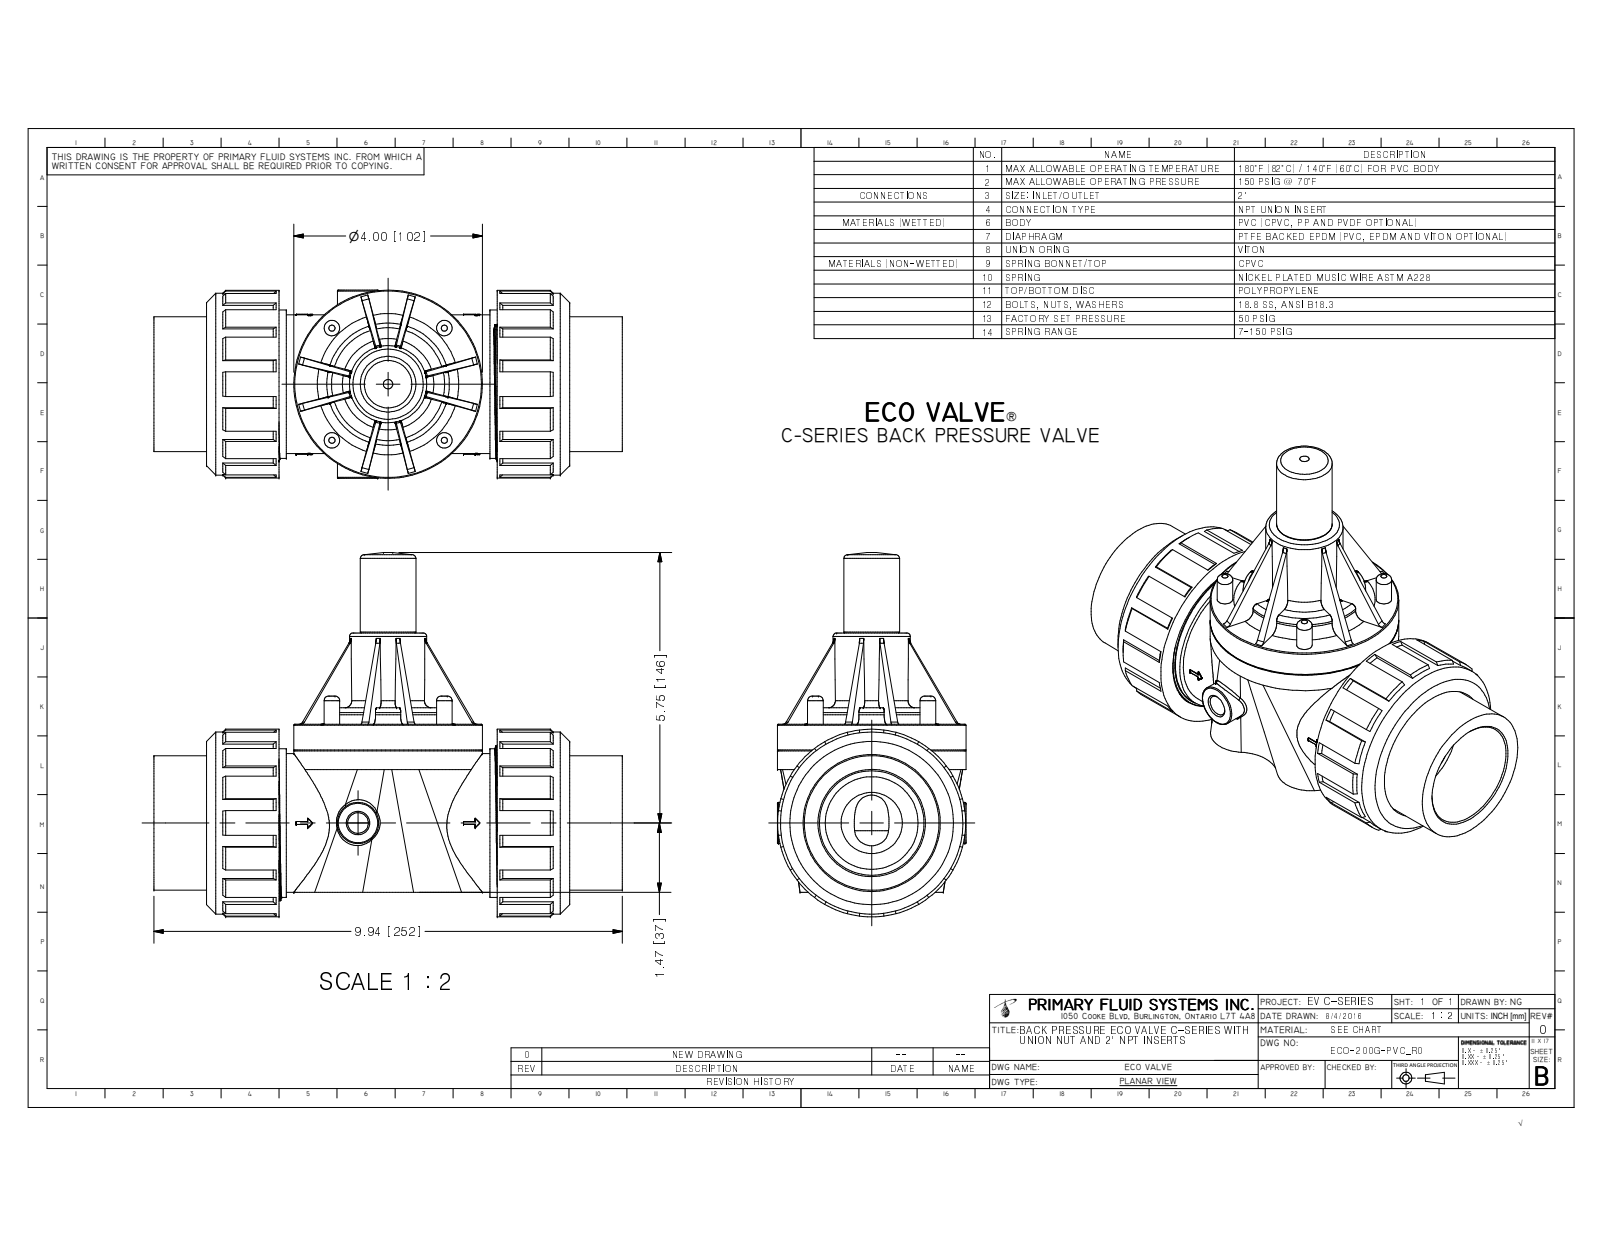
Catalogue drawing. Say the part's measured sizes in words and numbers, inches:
The part is named "ECO-200G-PVC_R0". Its 3-D file was written by "Autodesk Inventor 2009 (AUTOMOTIVE_DESIGN)". It is 1 solid with 576 faces: 242 planar, 99 cylindrical and 235 other. Overall it measures 9.94 by 7.744 by 4 inches. Its volume is 92.27 cubic inches and its surface area 269.8 square inches. Round holes: 4 of diameter 0.23, 1 of diameter 0.437, 1 of diameter 2.219, 1 of diameter 2.91. Round bosses or shafts: 4 of diameter 0.4, 4 of diameter 0.33, 1 of diameter 4, 1 of diameter 3.99, 1 of diameter 3.87, 1 of diameter 3.158, 1 of diameter 2.947, 1 of diameter 2.86. Partial cylindrical surfaces (rounded edges, fillets, slot ends): 15 of radius 0.1, 7 of radius 0.128, 4 of radius 0.05, 4 of radius 0.225, 1 of radius 0.412, 1 of radius 0.431, 1 of radius 0.471, 1 of radius 0.875. The main face-to-face distances are 1.155, 5.785, 0.385, 1.54, 6.17, 7.325, 1.115, 2.655, 1.5, 7.285. The hole center spacings are 2.385, 3.373.
